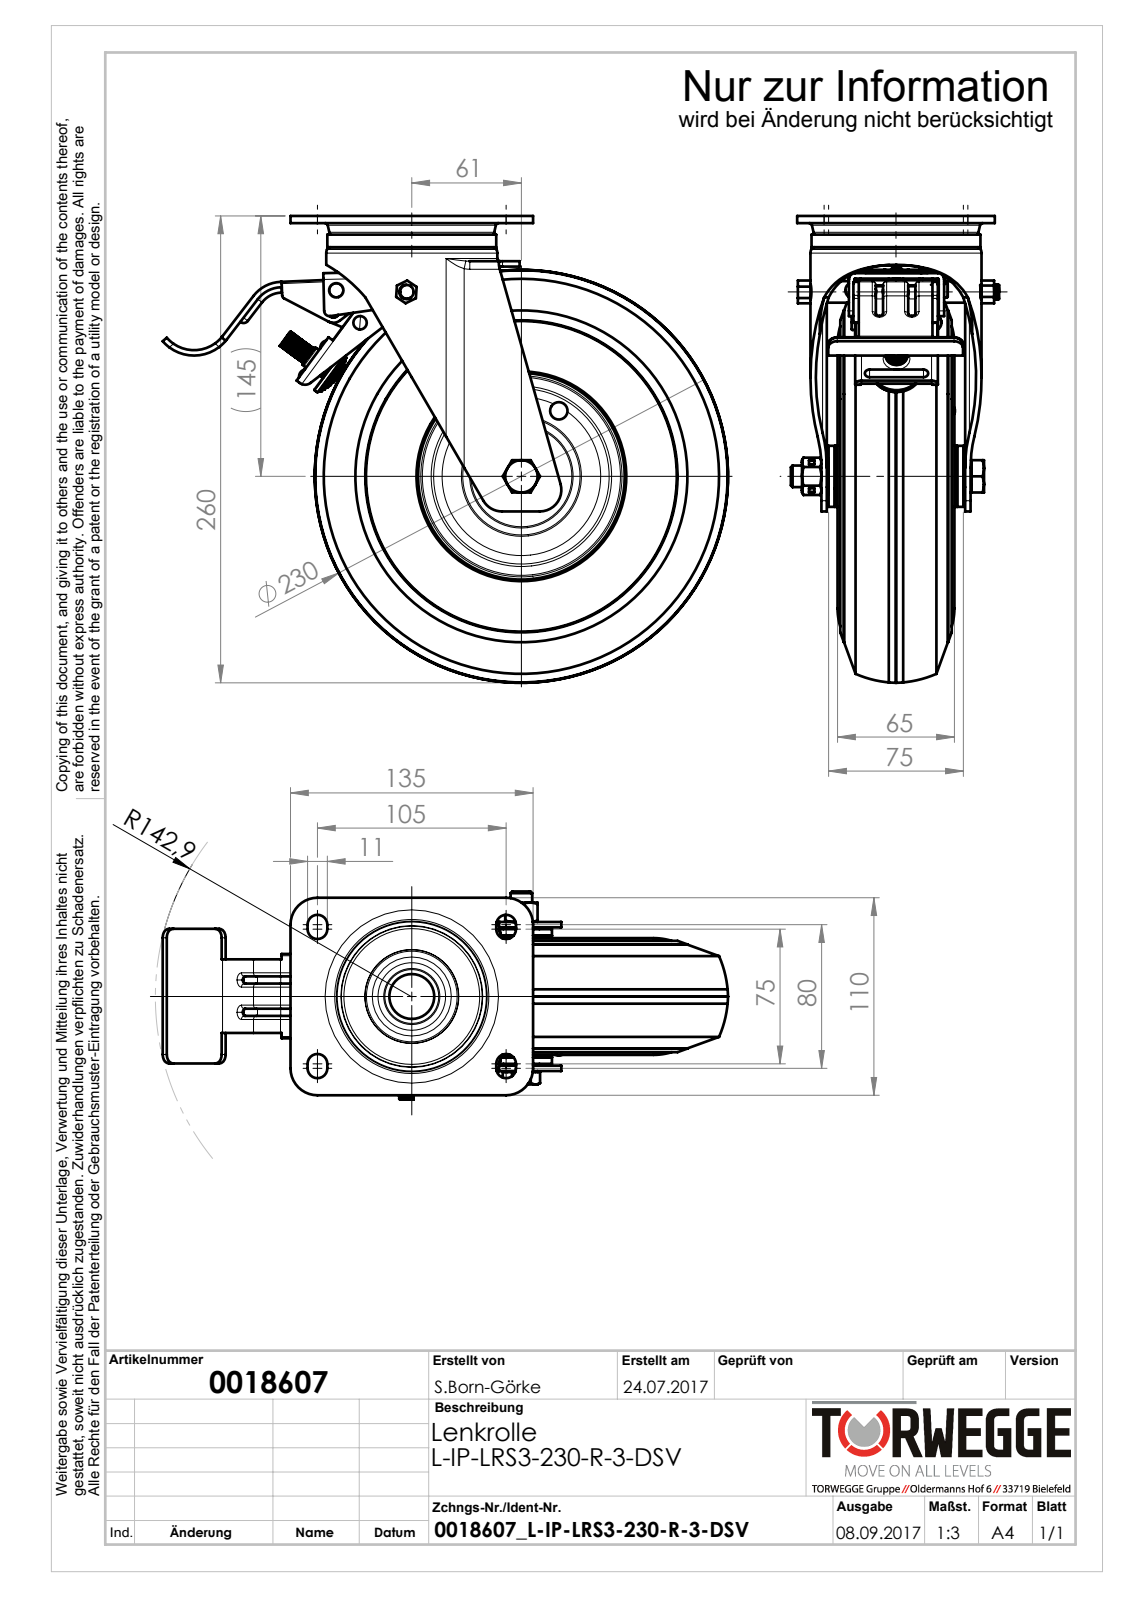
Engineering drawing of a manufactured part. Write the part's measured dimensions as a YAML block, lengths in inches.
part_name: "0018607_L-IP-LRS3-230-R-3-DSV"
step_written_by: "SolidWorks 2018 (AUTOMOTIVE_DESIGN)"
units: inches
bodies: {solids: 0, faces: 1410, planar: 507, cylindrical: 419, other: 484}
overall_size: [12.387, 10.236, 4.563]
round_holes:
  - {diameter: 0.248, count: 3}
  - {diameter: 0.157, count: 2}
  - {diameter: 0.244, count: 1}
  - {diameter: 0.268, count: 1}
  - {diameter: 0.319, count: 1}
  - {diameter: 0.323, count: 1}
  - {diameter: 0.394, count: 1}
  - {diameter: 0.402, count: 1}
  - {diameter: 0.453, count: 1}
  - {diameter: 0.472, count: 1}
  - {diameter: 0.48, count: 1}
  - {diameter: 0.492, count: 1}
round_bosses_or_shafts:
  - {diameter: 0.236, count: 4}
  - {diameter: 0.315, count: 3}
  - {diameter: 0.709, count: 2}
  - {diameter: 0.472, count: 2}
  - {diameter: 0.323, count: 2}
  - {diameter: 7.276, count: 1}
  - {diameter: 4.528, count: 1}
  - {diameter: 4.126, count: 1}
partial_cylinders:
  - {radius: 0.157, count: 22}
  - {radius: 0.079, count: 13}
  - {radius: 0.118, count: 11}
  - {radius: 0.039, count: 10}
  - {radius: 0.009, count: 9}
  - {radius: 0.019, count: 8}
  - {radius: 0.217, count: 8}
  - {radius: 0.028, count: 7}
face_to_face_distances: [0.118, 0.157, 3.15, 0.039, 1.634, 1.516, 1.083, 1.122, 3.031, 3.268]
hole_center_spacings: [0.315, 0.479, 0.63, 0.882, 1.024, 1.22, 1.339, 1.537]
